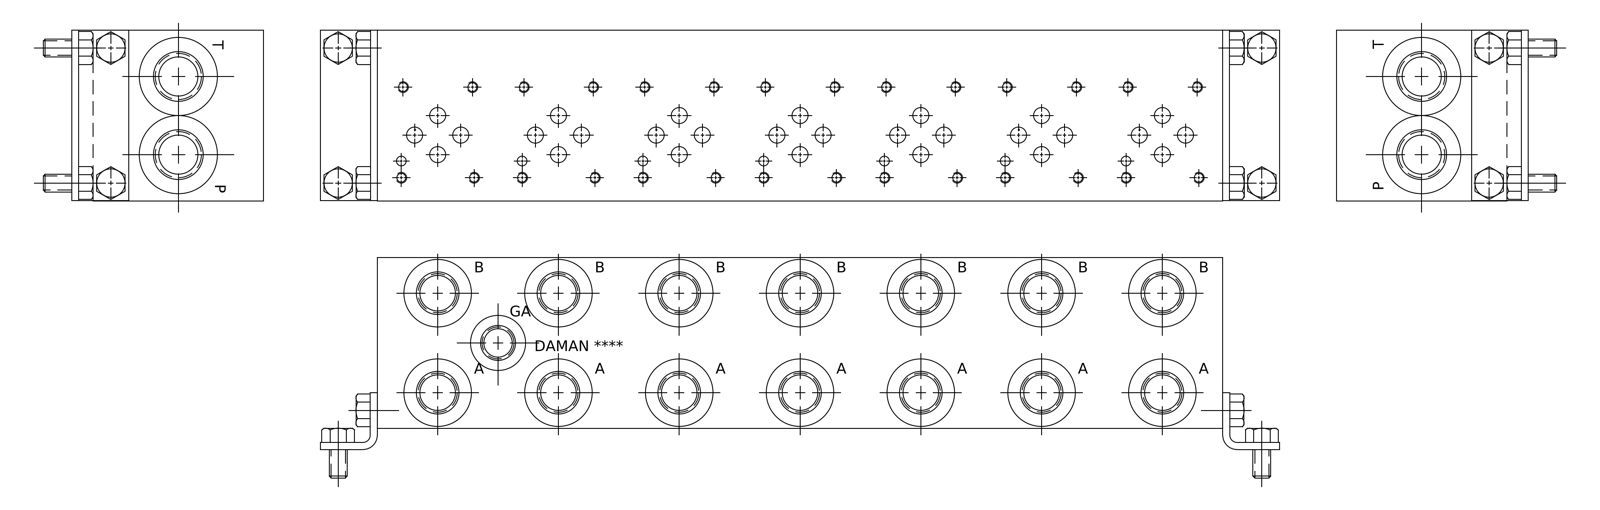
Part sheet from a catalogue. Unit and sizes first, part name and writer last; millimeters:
Units: millimetres
Overall size (bounding box): 377.82 × 76.2 × 76.2
Round holes (diameter × count): ⌀3.78 ×28, ⌀4.83 ×28, ⌀7.14 ×21, ⌀15.88 ×14, ⌀17.5 ×14, ⌀19.05 ×14, ⌀19.25 ×14, ⌀30.63 ×14, ⌀3.96 ×7, ⌀6.35 ×7, ⌀6.53 ×2, ⌀7.92 ×2
Main face-to-face distances: 76.2, 0.79, 75.41, 377.82, 377.04, 0.78, 376.25, 377.03, 14.27, 15.06
Hole centre spacings: 107.95, 53.98, 215.9, 53.97, 161.93, 161.92, 116.74, 118.61
Volume: 2 039 000 mm³ · Surface area: 165 291 mm²
Bodies: 1 solid, 1081 faces (522 planar, 194 cylindrical, 365 other)
Part name (STEP PRODUCT): Part_AD03P072S_3D
STEP written by: Autodesk Inventor 2020 (AUTOMOTIVE_DESIGN)
